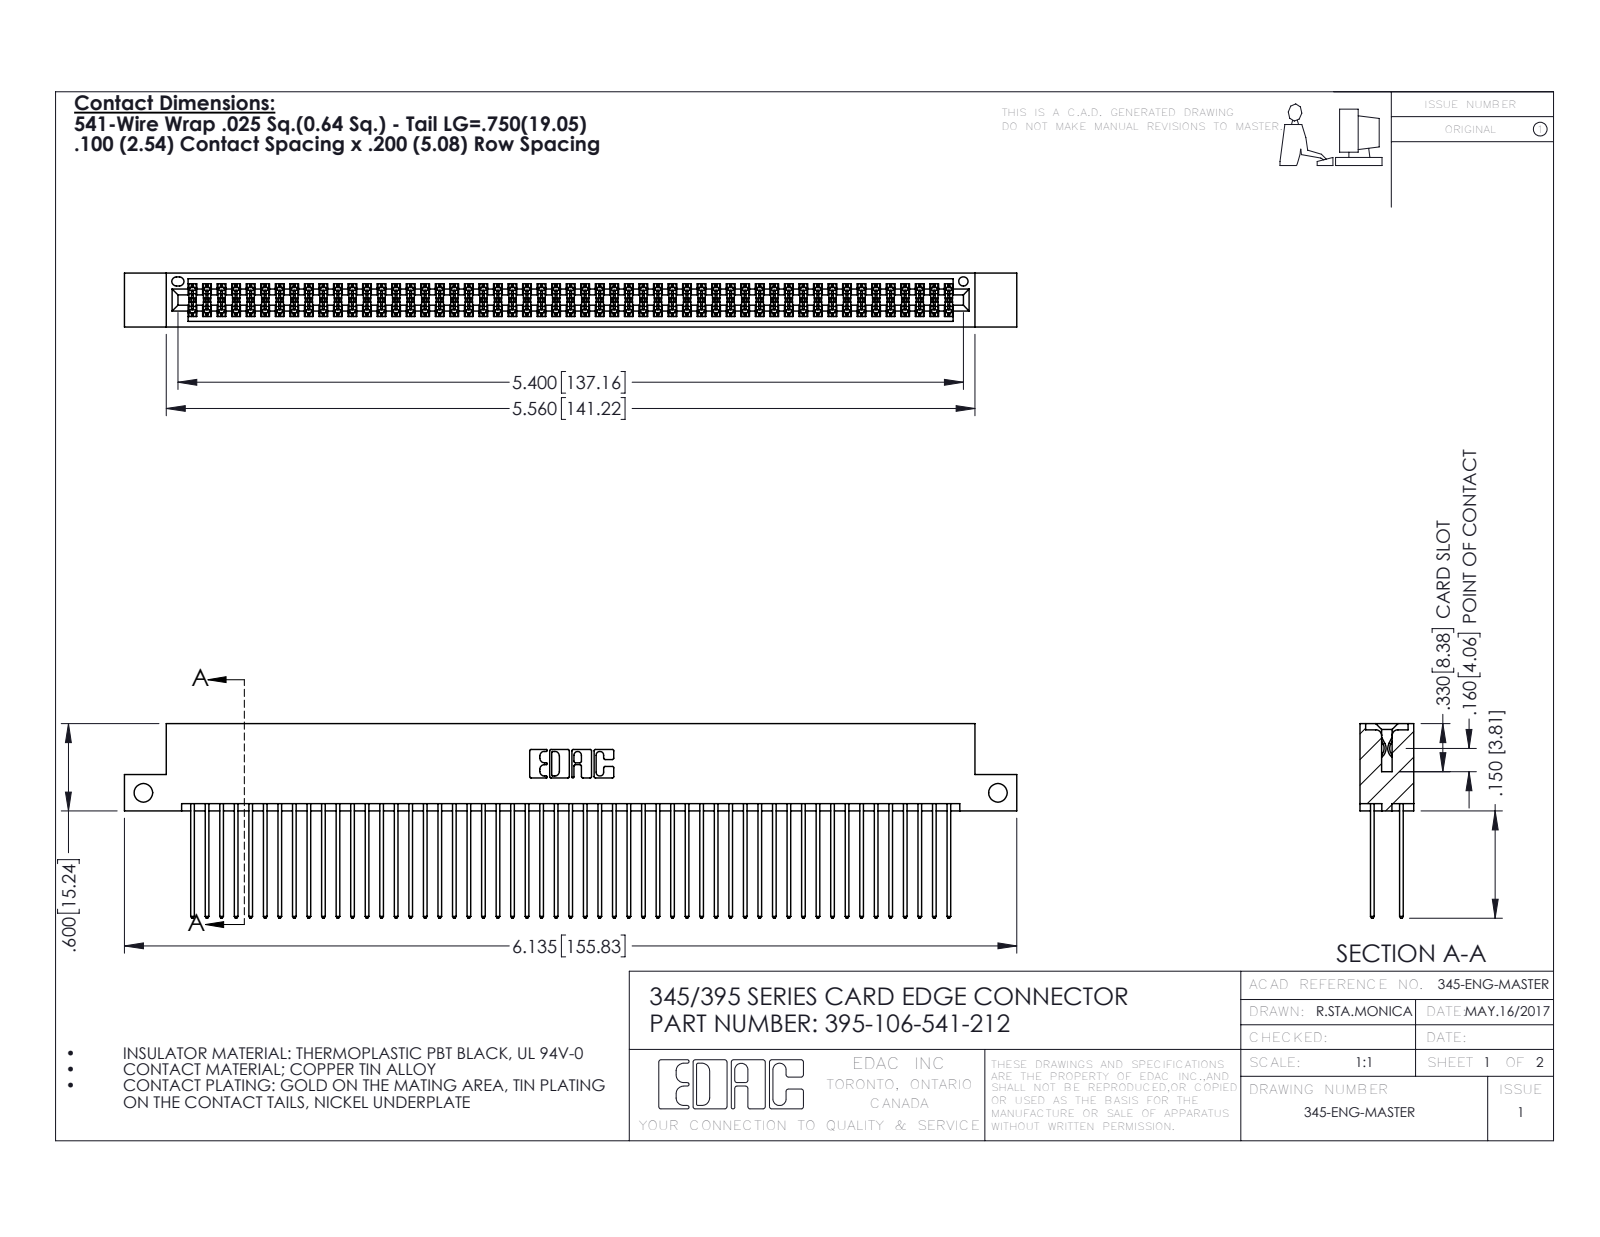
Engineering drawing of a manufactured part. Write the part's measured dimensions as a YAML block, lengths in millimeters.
part_name: "345-292-001_345-293-141; 395-106-541-212; 345 Part_Flush Mounting Lugs - Side Mount"
step_written_by: "SolidWorks 2016 (CONFIG_CONTROL_DESIGN)"
units: millimeters
bodies: {solids: 107, faces: 5426, planar: 3578, cylindrical: 1848, other: 0}
overall_size: [155.8, 34, 9.4]
volume: 15800
surface_area: 26230
round_holes:
  - {diameter: 3.3, count: 2}
  - {diameter: 1.6, count: 1}
partial_cylinders:
  - {radius: 0.2, count: 159}
  - {radius: 0.3, count: 106}
  - {radius: 0.3, count: 22}
  - {radius: 0.2, count: 6}
  - {radius: 0.8, count: 6}
  - {radius: 0.7, count: 3}
  - {radius: 0.4, count: 2}
  - {radius: 0.5, count: 2}
face_to_face_distances: [7.6, 1.8, 5.1, 2.5, 6.9, 0.6, 5.7, 9.4, 4.4, 3.8]
hole_center_spacings: [149.2]
